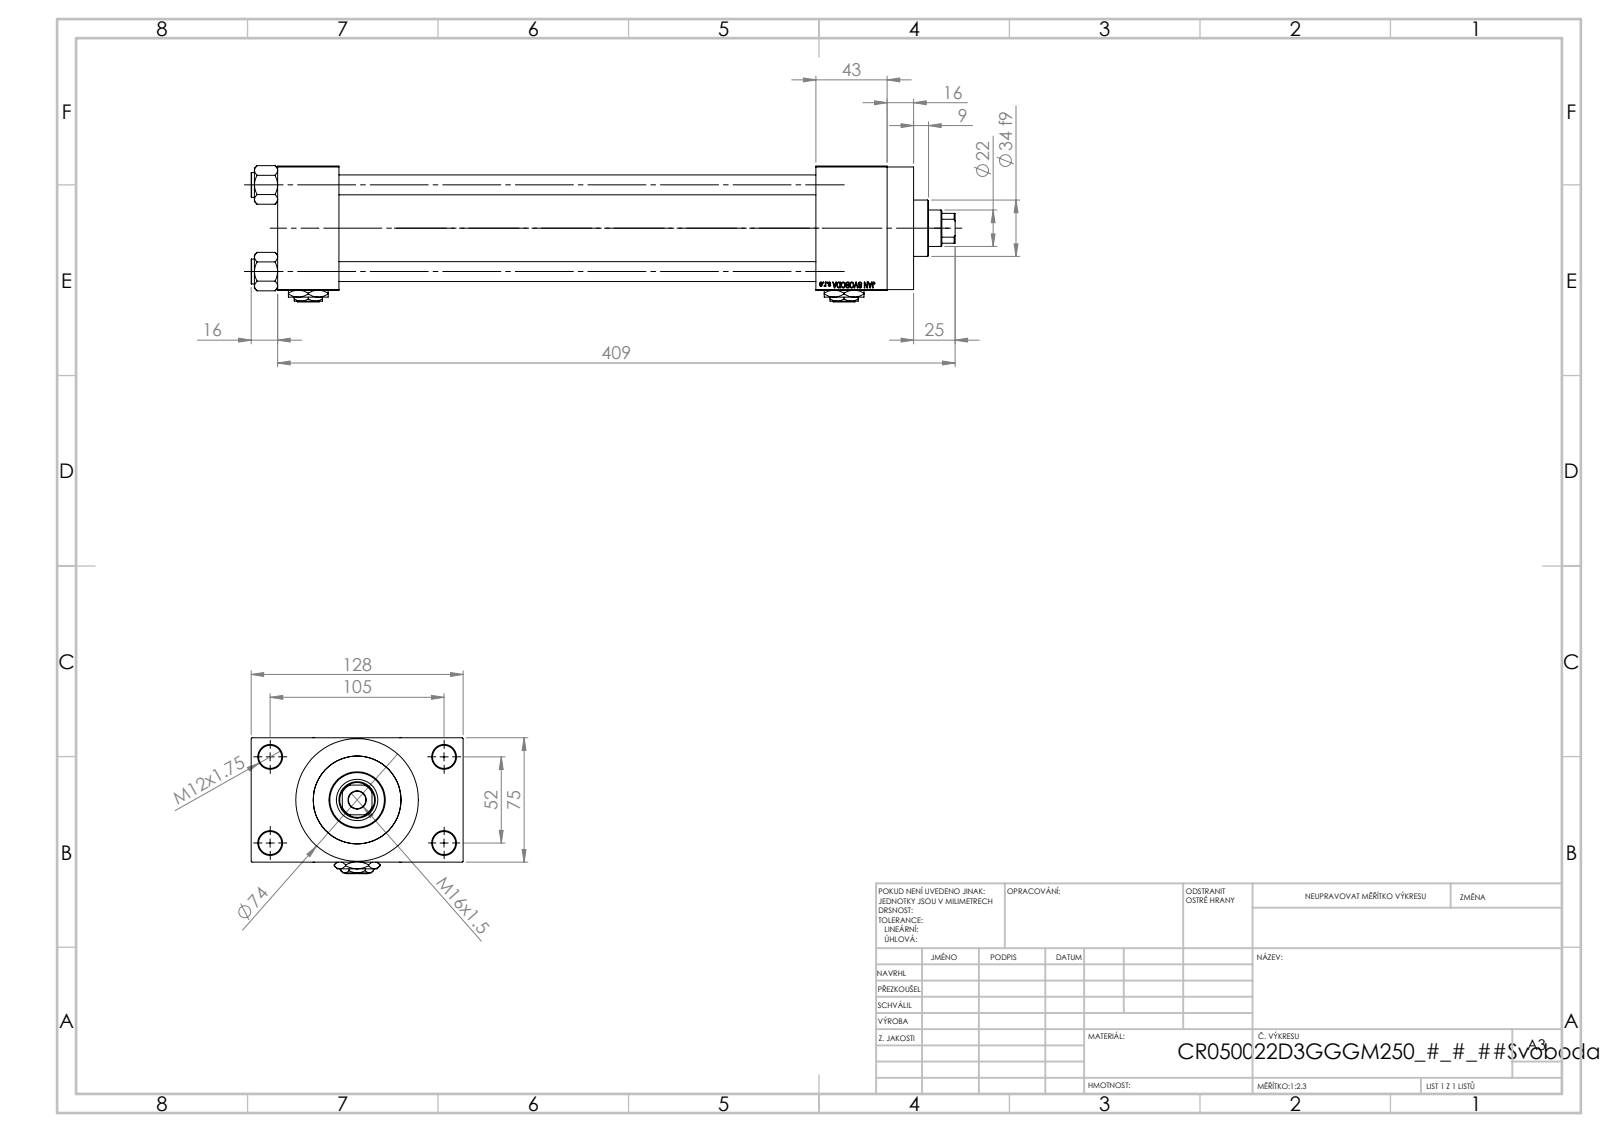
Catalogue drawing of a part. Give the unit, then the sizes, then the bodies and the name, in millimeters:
Units: millimetres
Overall size (bounding box): 425 × 128 × 82.27
Round holes (diameter × count): ⌀12 ×4, ⌀14 ×4, ⌀7 ×2, ⌀20.96 ×2, ⌀30 ×2, ⌀10.5 ×1, ⌀22 ×1, ⌀25 ×1, ⌀41 ×1, ⌀50 ×1, ⌀53 ×1
Round bosses / shafts (diameter × count): ⌀15 ×4, ⌀74 ×1, ⌀56 ×1, ⌀34 ×1
Partial cylindrical surfaces — rounded edges, fillets, slot ends (radius × count): R10.5 ×1
Main face-to-face distances: 75, 288, 37, 325, 26.5, 101.5, 368, 331, 43, 16
Hole centre spacings: 26.35, 36.98, 52.3, 58.43, 58.59, 78.65, 94.37, 52
Volume: 1 109 000 mm³ · Surface area: 296 355 mm²
Bodies: 13 solids, 1205 faces (545 planar, 100 cylindrical, 560 other)
Part name (STEP PRODUCT): V215CR_D_TYCINKA; NUT_M5_D; V215_VC_A; Zatka_pro_OIL_PORT (+2 more)
STEP written by: SolidWorks 2019 (CONFIG_CONTROL_DESIGN)
